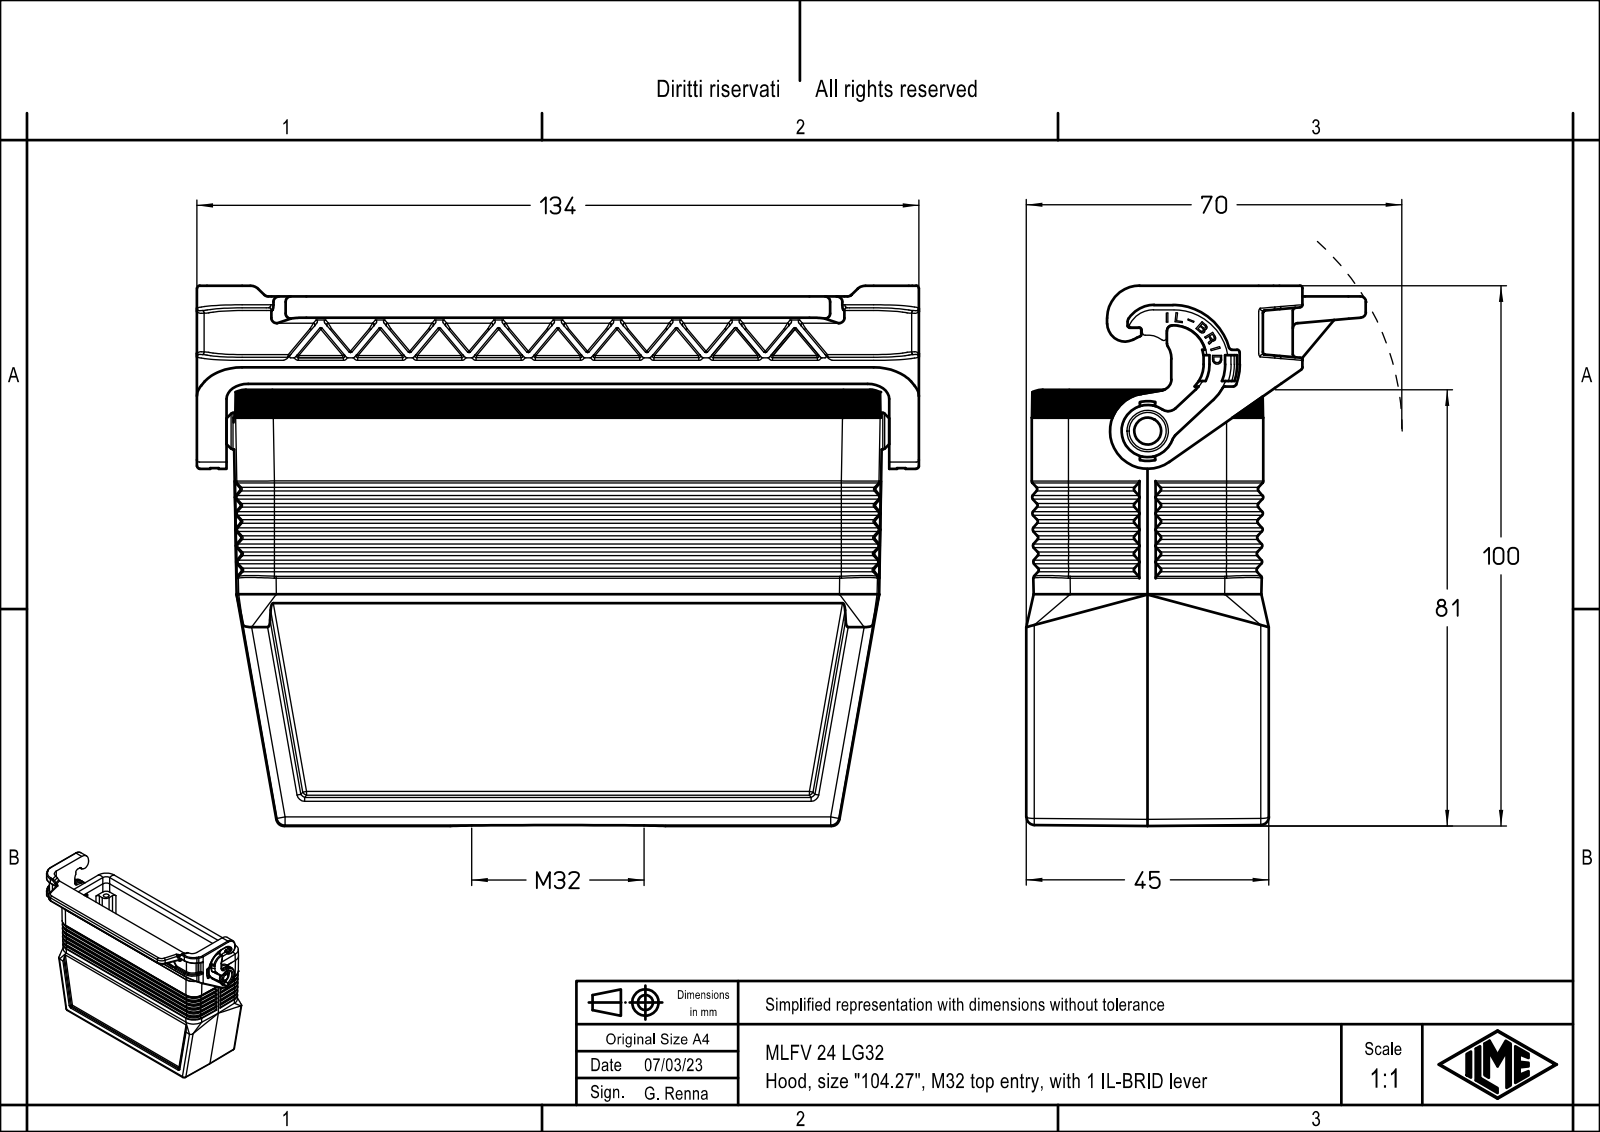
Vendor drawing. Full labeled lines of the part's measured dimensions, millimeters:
Part name (STEP PRODUCT): MLFV 24 LG40; MLFV 24 LG32
STEP written by: Creo Elements/Direct Modeling 20.1B 02-Apr-2019 (C) Parametric Technology GmbH (AUTOMOTIVE_DESIGN)
Units: millimetres
Bodies: 1 solid, 1364 faces (797 planar, 369 cylindrical, 198 other)
Overall size (bounding box): 134 × 100.25 × 63
Volume: 130 394 mm³ · Surface area: 71 502 mm²
Round holes (diameter × count): ⌀3 ×4, ⌀3.5 ×4, ⌀3.25 ×1, ⌀5.4 ×1, ⌀7.7 ×1, ⌀32.5 ×1
Round bosses / shafts (diameter × count): ⌀6.9 ×1, ⌀6.8 ×1, ⌀5.2 ×1, ⌀3.2 ×1
Partial cylindrical surfaces — rounded edges, fillets, slot ends (radius × count): R0.5 ×77, R0.1 ×27, R1.5 ×23, R1 ×16, R0.2 ×15, R7 ×14, R0.33 ×13, R0.55 ×12
Main face-to-face distances: 3.75, 39.25, 35.5, 43, 2, 7, 46.25, 3.25, 42.5, 1
Hole centre spacings: 53.72, 27, 104, 107.45
